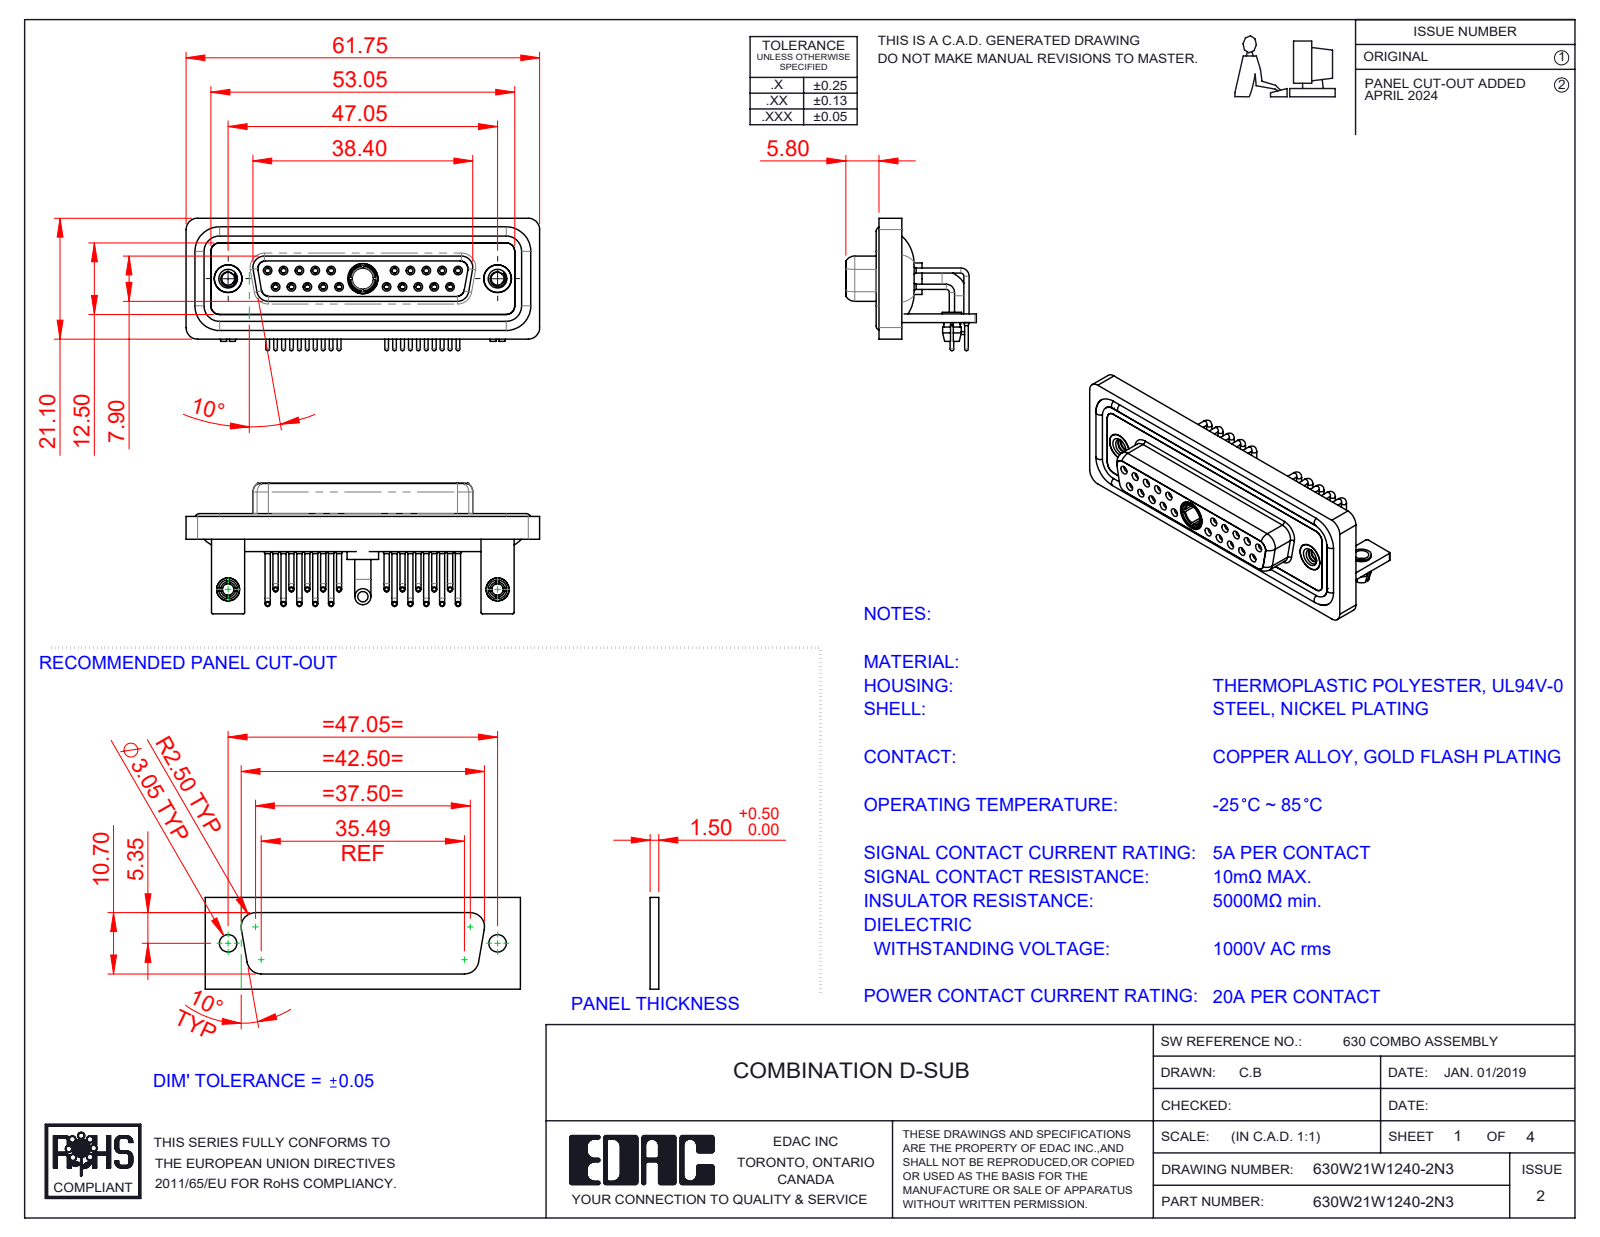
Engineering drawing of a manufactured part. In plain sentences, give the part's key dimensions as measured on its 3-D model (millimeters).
The part is named "630Combo Housing_21W1; 630W21W1240-2N3; 630Combo Stabilizer Bracket_50 Contacts; 630Combo Contact Row 2_50 Contacts (+7 more)". Its 3-D file was written by "SolidWorks 2023 (CONFIG_CONTROL_DESIGN)". It is 33 solids with 1664 faces: 502 planar, 729 cylindrical and 433 other. Overall it measures 61.75 by 23.12 by 22.8 millimeters. Its volume is 8 908 cubic millimeters and its surface area 15 725 square millimeters. Round holes: 22 of diameter 2, 20 of diameter 0.9, 20 of diameter 1.1, 20 of diameter 1.5, 10 of diameter 1.6, 10 of diameter 1.7, 3 of diameter 4.85, 2 of diameter 2.26, 2 of diameter 2.5, 2 of diameter 3.2, 2 of diameter 4, 2 of diameter 4.05. Round bosses or shafts: 20 of diameter 0.9, 20 of diameter 0.65, 14 of diameter 1.6, 2 of diameter 4.95, 2 of diameter 4.8, 2 of diameter 4, 2 of diameter 3.4, 2 of diameter 3.3. Partial cylindrical surfaces (rounded edges, fillets, slot ends): 19 of radius 2, 18 of radius 1.5, 16 of radius 0.25, 8 of radius 1.35, 8 of radius 1.6, 5 of radius 0.5, 4 of radius 0.6, 4 of radius 0.65. The main face-to-face distances are 0.4, 1.8, 2.9, 3.7, 1.5, 4.1, 1.1, 1.4, 1.6, 2.5. The hole center spacings are 3.16, 2.77, 5.54, 8.31, 5.04, 19.39, 20.97, 22.16.
